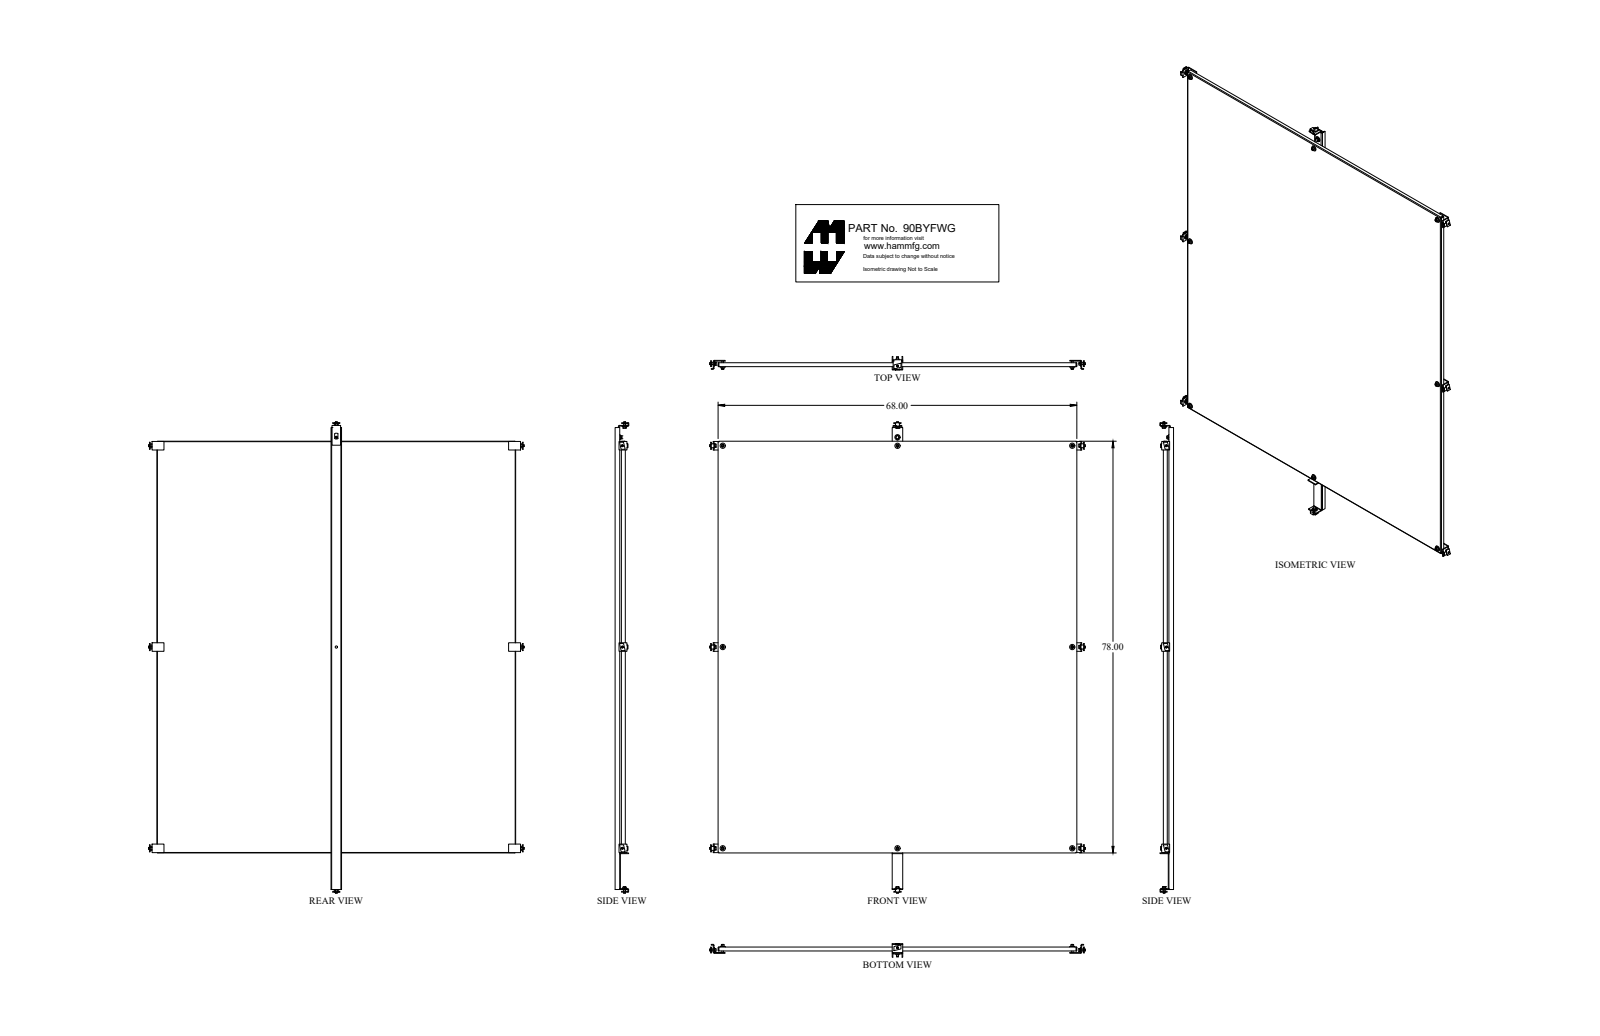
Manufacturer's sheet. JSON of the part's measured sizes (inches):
{"part_name": "90BYFWG_Default", "step_written_by": "SolidWorks 2018 (CONFIG_CONTROL_DESIGN)", "units": "inches", "bodies": {"solids": 18, "faces": 385, "planar": 188, "cylindrical": 133, "other": 64}, "overall_size": [88.906, 70.582, 2.593], "volume_in3": 567.2, "surface_area_in2": 11771, "round_holes": [[0.563, 8], [0.437, 6], [0.437, 1], [0.453, 1]], "round_bosses_or_shafts": [[0.65, 8], [0.33, 8], [0.375, 5], [0.375, 3]], "partial_cylinders_radius": [[0.06, 11], [0.185, 11], [0.048, 4], [0.143, 4], [0.219, 2]], "face_to_face_distances": [0.095, 0.125, 1.187, 1.062, 0.967, 1.092, 33, 35, 67.905, 32.905], "hole_center_spacings": [50.505, 33.125, 33.125, 38.125, 38.125, 66.25, 76.25, 38.13]}
